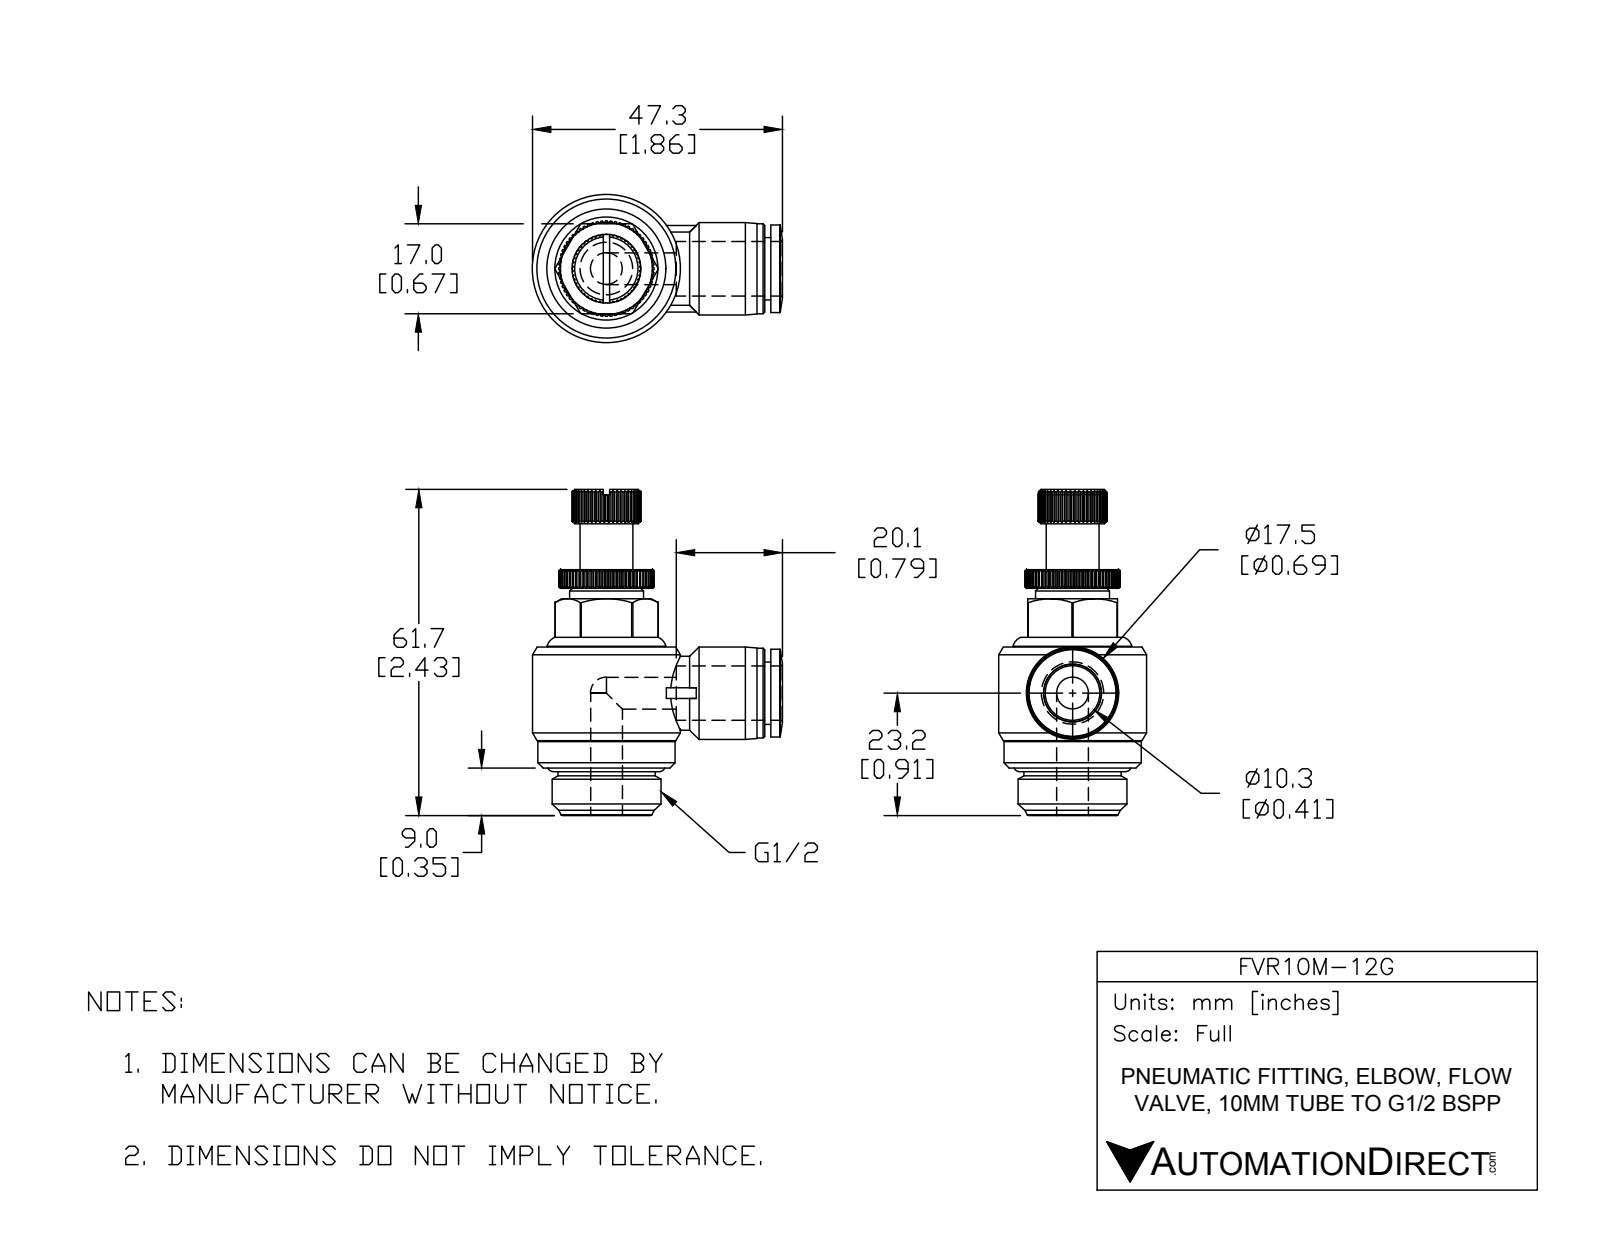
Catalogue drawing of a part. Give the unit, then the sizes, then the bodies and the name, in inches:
Units: inches
Overall size (bounding box): 2.429 × 1.862 × 1.102
Round holes (diameter × count): ⌀0.236 ×2, ⌀0.406 ×1
Round bosses / shafts (diameter × count): ⌀0.551 ×2, ⌀1.102 ×1, ⌀1.024 ×1, ⌀0.945 ×1, ⌀0.864 ×1, ⌀0.811 ×1, ⌀0.724 ×1, ⌀0.689 ×1
Partial cylindrical surfaces — rounded edges, fillets, slot ends (radius × count): R0.256 ×1, R0.354 ×1, R0.384 ×1
Main face-to-face distances: 0.669, 1.256, 1.831, 0.575, 0.705, 1.693, 0.437, 0.138, 0.045, 2.429
Volume: 1.403 in³ · Surface area: 13.39 in²
Bodies: 2 solids, 601 faces (263 planar, 153 cylindrical, 185 other)
Part name (STEP PRODUCT): FVR10M-12G
STEP written by: SolidWorks 2015 (AUTOMOTIVE_DESIGN)
